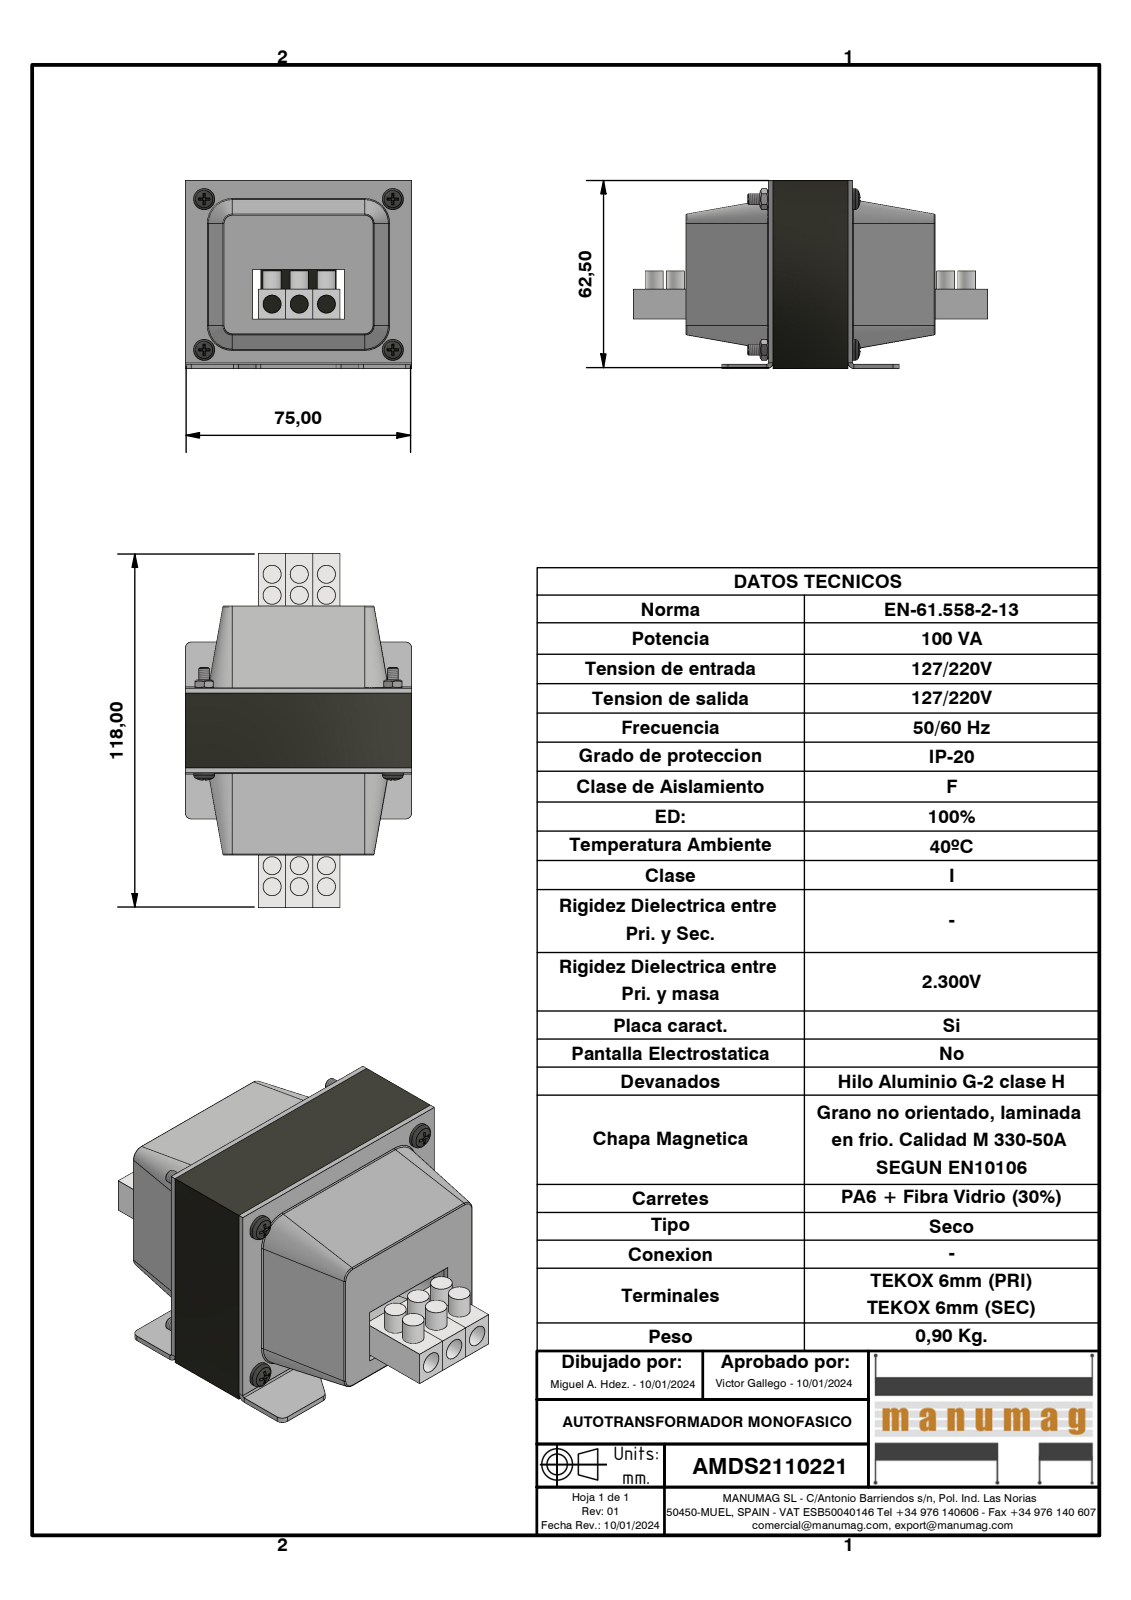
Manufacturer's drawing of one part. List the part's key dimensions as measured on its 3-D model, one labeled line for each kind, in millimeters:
Part name (STEP PRODUCT): AMDS2110221; DIN EN ISO 7045 - M3,5 x 35 - 4.8 - H; DIN 934 - M3,5 x 0,6; EI75 x 62,5 - 25 (RC25) Negro (+3 more)
STEP written by: Autodesk Inventor 2023 (AUTOMOTIVE_DESIGN)
Units: millimetres
Bodies: 17 solids, 392 faces (194 planar, 74 cylindrical, 124 other)
Overall size (bounding box): 118 × 75 × 62.5
Volume: 118 666 mm³ · Surface area: 70 955 mm²
Round holes (diameter × count): ⌀2.85 ×4, ⌀3 ×4, ⌀4.5 ×4, ⌀6 ×3
Round bosses / shafts (diameter × count): ⌀6 ×12, ⌀3.5 ×4, ⌀3.18 ×4
Partial cylindrical surfaces — rounded edges, fillets, slot ends (radius × count): R0.38 ×16, R2 ×14, R0.5 ×2
Main face-to-face distances: 25, 1.5, 27.5, 54, 12.5, 53.58, 50, 62.5, 63.43, 26.5
Hole centre spacings: 9, 50, 62.5, 80.04, 18, 26.73, 27.14, 34.52
